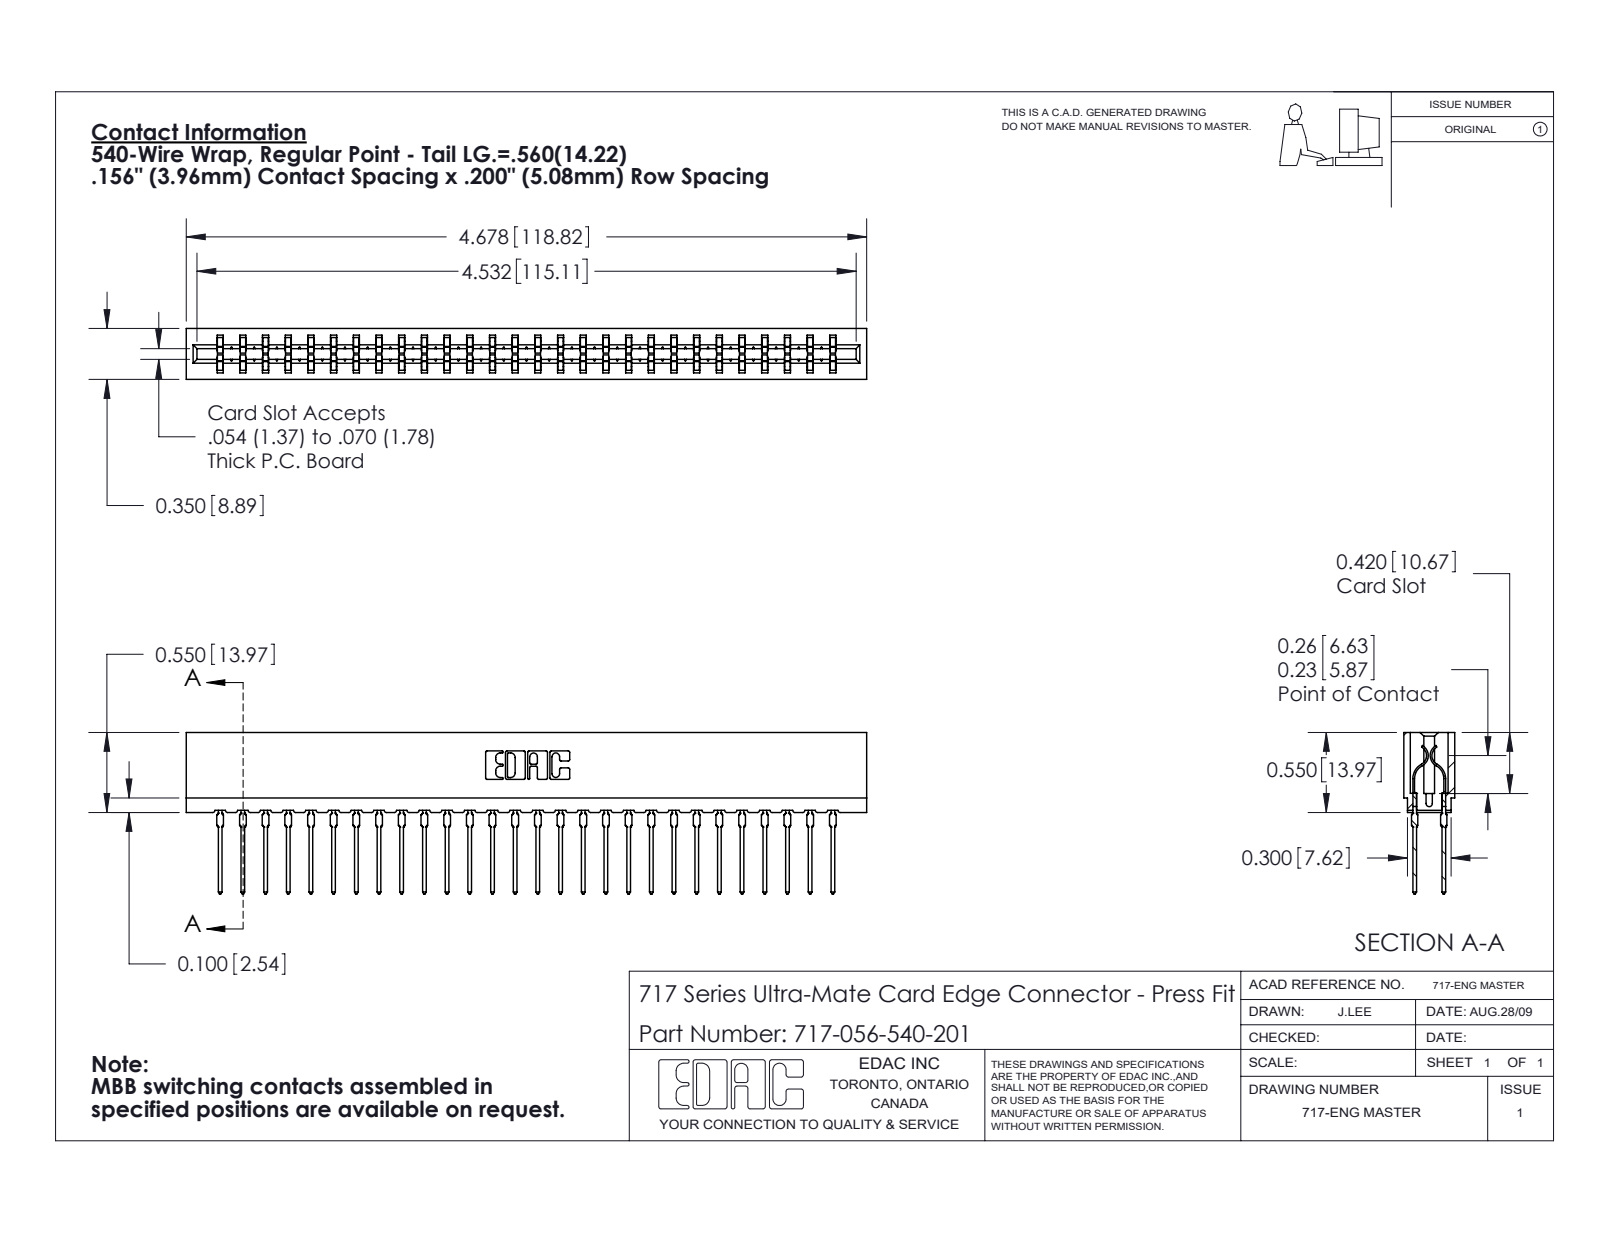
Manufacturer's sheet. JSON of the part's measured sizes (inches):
{"part_name": "717-056-540-201; 717 Part_Insulator Option - 06; 745-292-001_540", "step_written_by": "SolidWorks 2020 (CONFIG_CONTROL_DESIGN)", "units": "inches", "bodies": {"solids": 57, "faces": 5134, "planar": 2658, "cylindrical": 1020, "other": 1456}, "overall_size": [4.678, 1.109, 0.35], "volume_in3": 0.642, "surface_area_in2": 25.78, "partial_cylinders_radius": [[0.021, 112], [0.015, 56], [0.01, 22], [0.005, 8], [0.011, 8], [0.007, 6], [0.031, 6], [0.026, 3]], "face_to_face_distances": [0.212, 0.138, 0.35, 0.063, 0.287, 0.076, 0.149, 0.074, 0.087, 0.263]}
